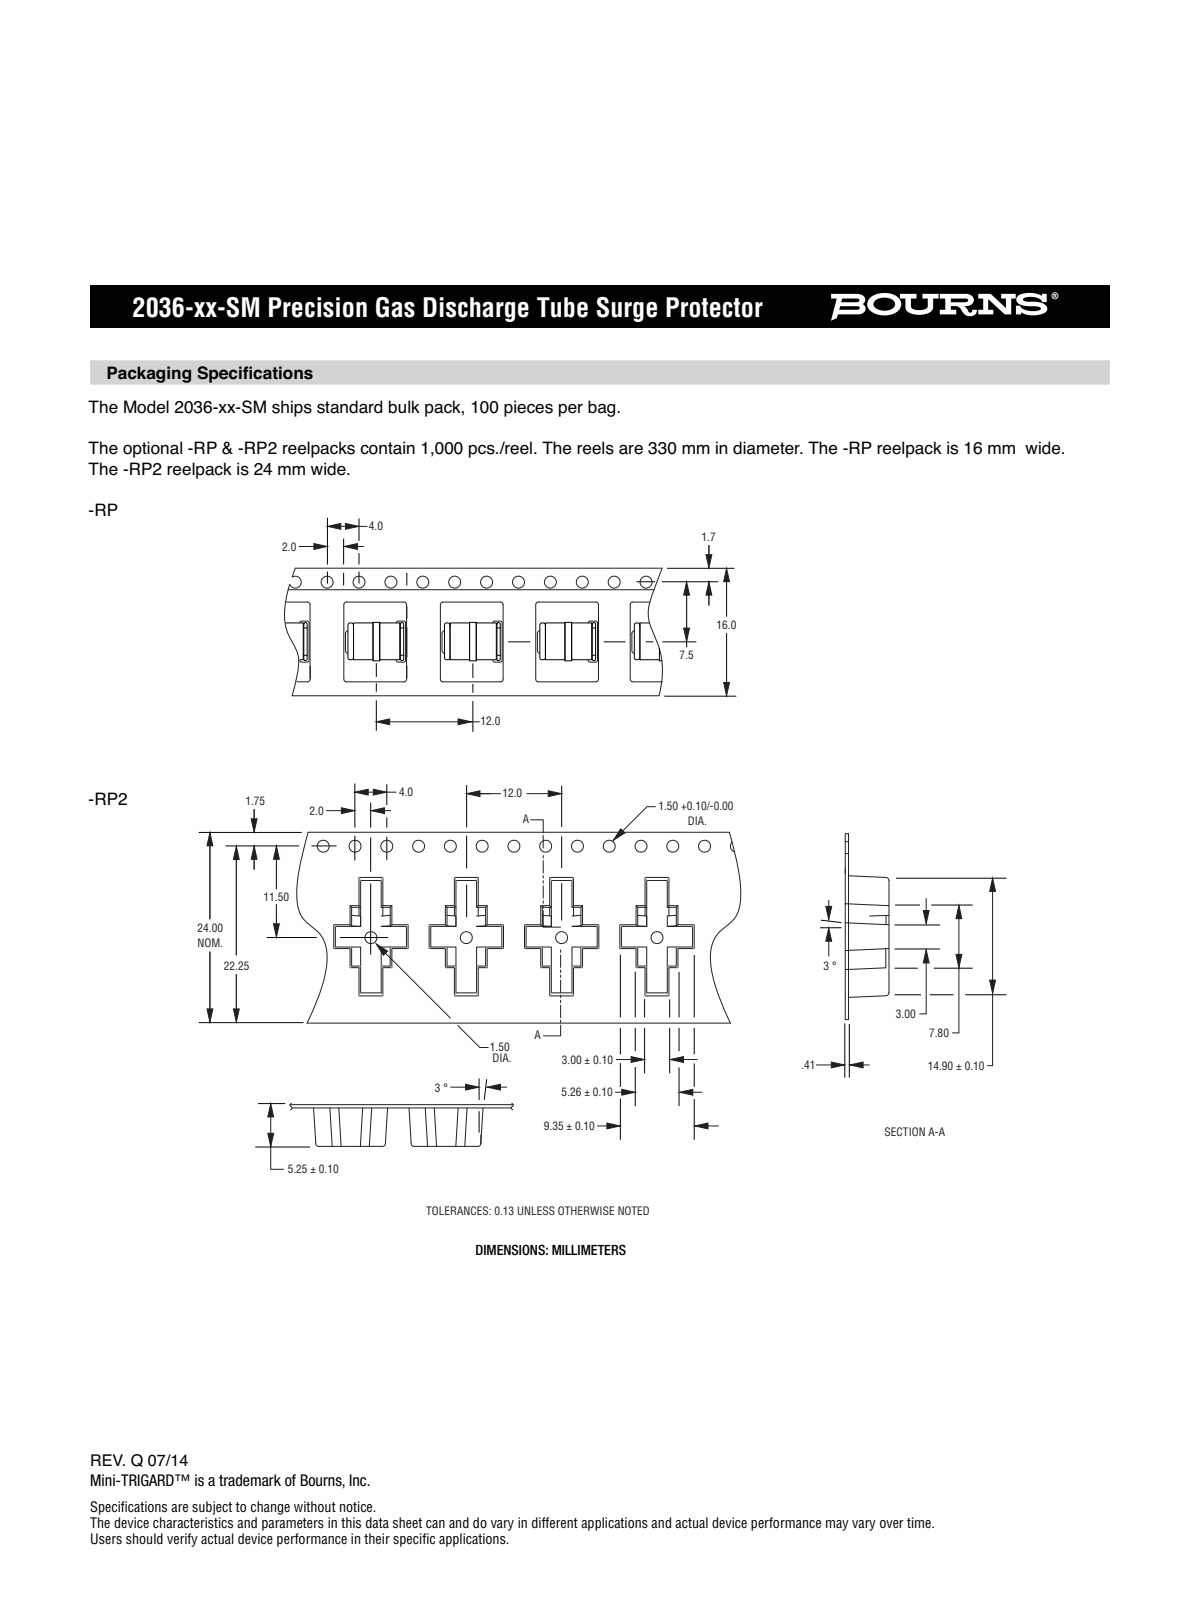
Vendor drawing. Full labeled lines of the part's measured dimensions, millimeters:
Part name (STEP PRODUCT): 2036-XX-SM; 65506_F; 34436-XX-CU; 34466-XX-CH (+2 more)
STEP written by: SolidWorks 2019 (AUTOMOTIVE_DESIGN)
Units: millimetres
Bodies: 7 solids, 257 faces (149 planar, 56 cylindrical, 52 other)
Overall size (bounding box): 7 × 5 × 5
Volume: 100 mm³ · Surface area: 397 mm²
Round holes (diameter × count): ⌀1.3 ×1, ⌀2 ×1, ⌀2 ×1, ⌀2.3 ×1, ⌀3.6 ×1, ⌀3.6 ×1
Round bosses / shafts (diameter × count): ⌀5 ×1, ⌀4.9 ×1, ⌀4.7 ×1, ⌀3.4 ×1, ⌀3.3 ×1, ⌀2.6 ×1, ⌀2.5 ×1, ⌀1.8 ×1
Partial cylindrical surfaces — rounded edges, fillets, slot ends (radius × count): R0.1 ×8, R3 ×1, R3 ×1
Main face-to-face distances: 2.6, 3.4, 2.6, 3.5, 6.1, 3.1, 0.9, 4, 0.5, 0.6
